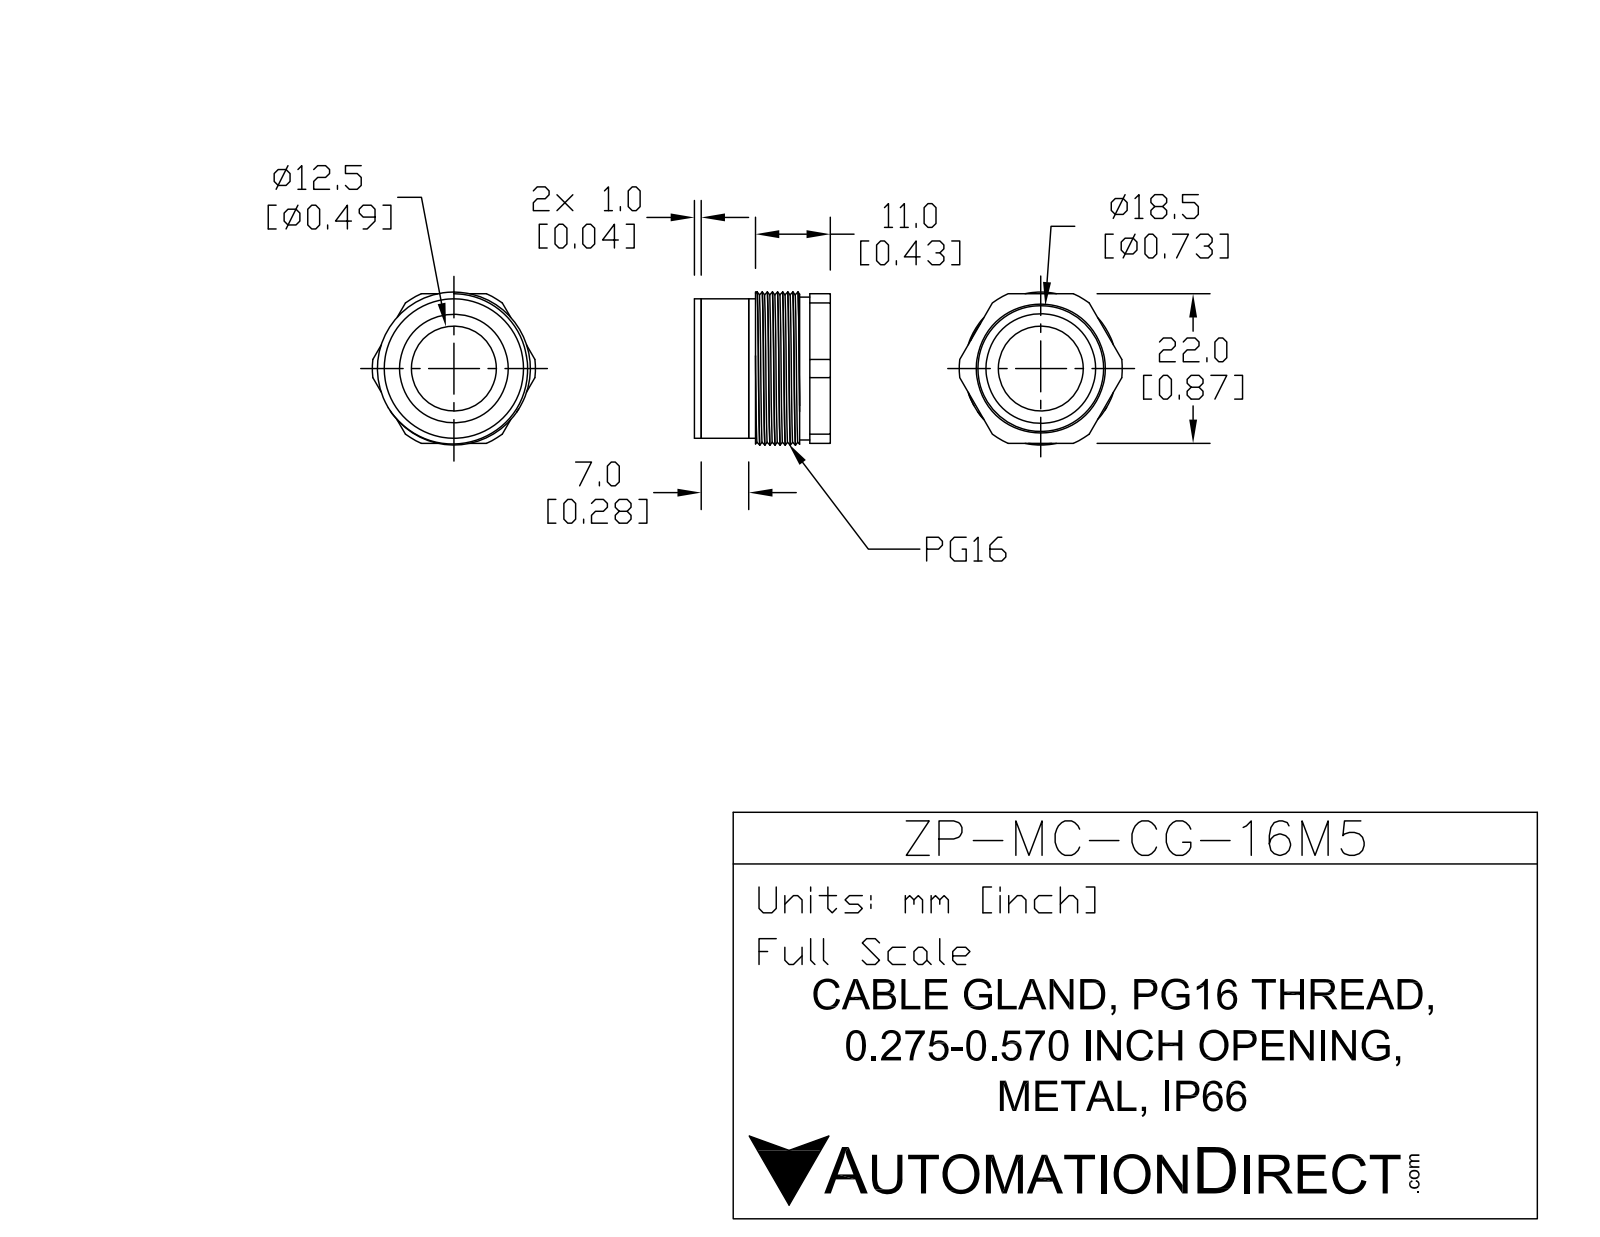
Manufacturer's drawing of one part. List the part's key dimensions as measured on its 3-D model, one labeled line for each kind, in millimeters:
Part name (STEP PRODUCT): ZP-MC-CG-16M5
STEP written by: SolidWorks 2011 (AUTOMOTIVE_DESIGN)
Units: millimetres
Bodies: 3 solids, 36 faces (17 planar, 15 cylindrical, 4 other)
Overall size (bounding box): 24 × 22.5 × 20
Volume: 2 944 mm³ · Surface area: 3 749 mm²
Round holes (diameter × count): ⌀12.5 ×1, ⌀16 ×1, ⌀16.15 ×1, ⌀18.5 ×1
Round bosses / shafts (diameter × count): ⌀22.5 ×1, ⌀21 ×1, ⌀20.5 ×1
Partial cylindrical surfaces — rounded edges, fillets, slot ends (radius × count): R12 ×1
Main face-to-face distances: 7, 8, 1, 9, 11, 12, 19, 20, 22, 3
